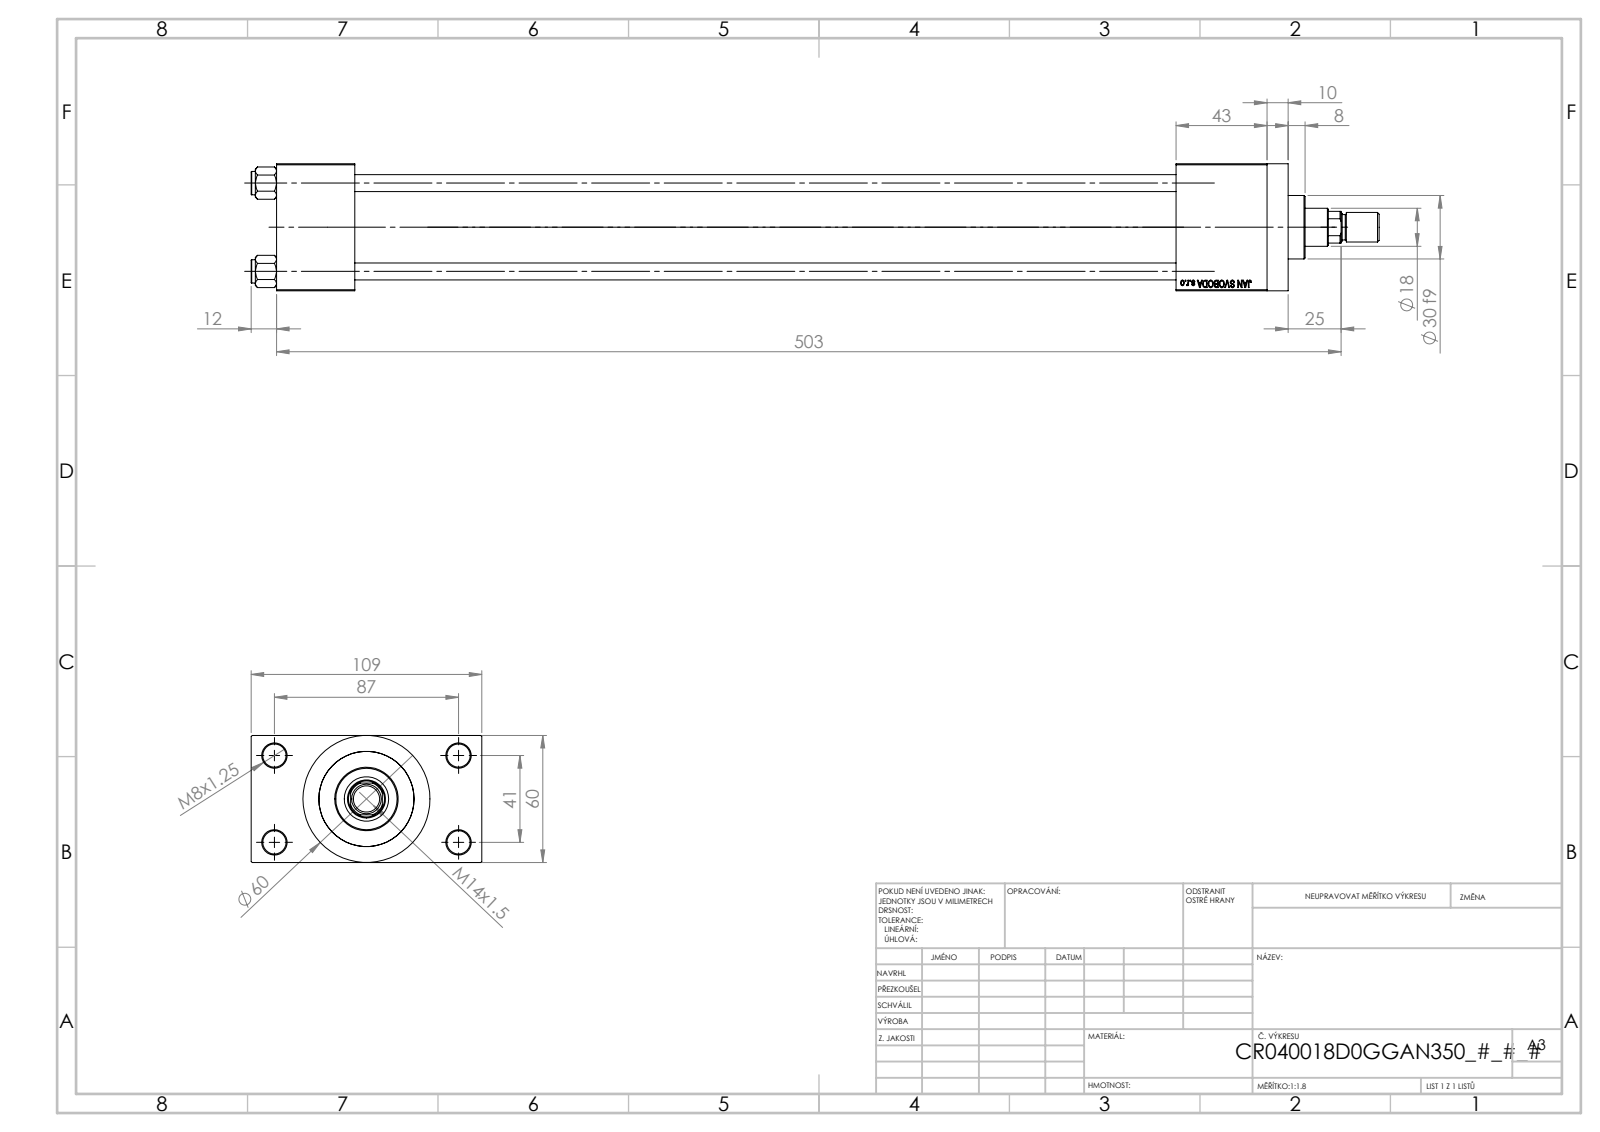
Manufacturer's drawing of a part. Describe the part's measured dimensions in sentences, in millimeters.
The part is named "V215CR_D_TYCINKA; NUT_M5_D; V215CR_VCP_D; ROD_END_AH (+2 more)". Its 3-D file was written by "SolidWorks 2019 (CONFIG_CONTROL_DESIGN)". It is 12 solids with 1119 faces: 502 planar, 93 cylindrical and 524 other. Overall it measures 533 by 109 by 60 millimeters. Its volume is 804 501 cubic millimeters and its surface area 263 388 square millimeters. Round holes: 4 of diameter 8, 4 of diameter 11, 2 of diameter 7, 2 of diameter 16.66, 2 of diameter 24, 1 of diameter 8.5, 1 of diameter 18, 1 of diameter 21, 1 of diameter 31, 1 of diameter 40, 1 of diameter 45. Round bosses or shafts: 4 of diameter 11, 1 of diameter 60, 1 of diameter 46, 1 of diameter 30, 1 of diameter 14, 1 of diameter 12. Partial cylindrical surfaces (rounded edges, fillets, slot ends): 1 of radius 8.5. The main face-to-face distances are 60, 24.5, 84.5, 388, 37, 425, 43, 468, 431, 109. The hole center spacings are 22.65, 29.49, 41.7, 47.15, 48.09, 64.35, 76.49, 41.
